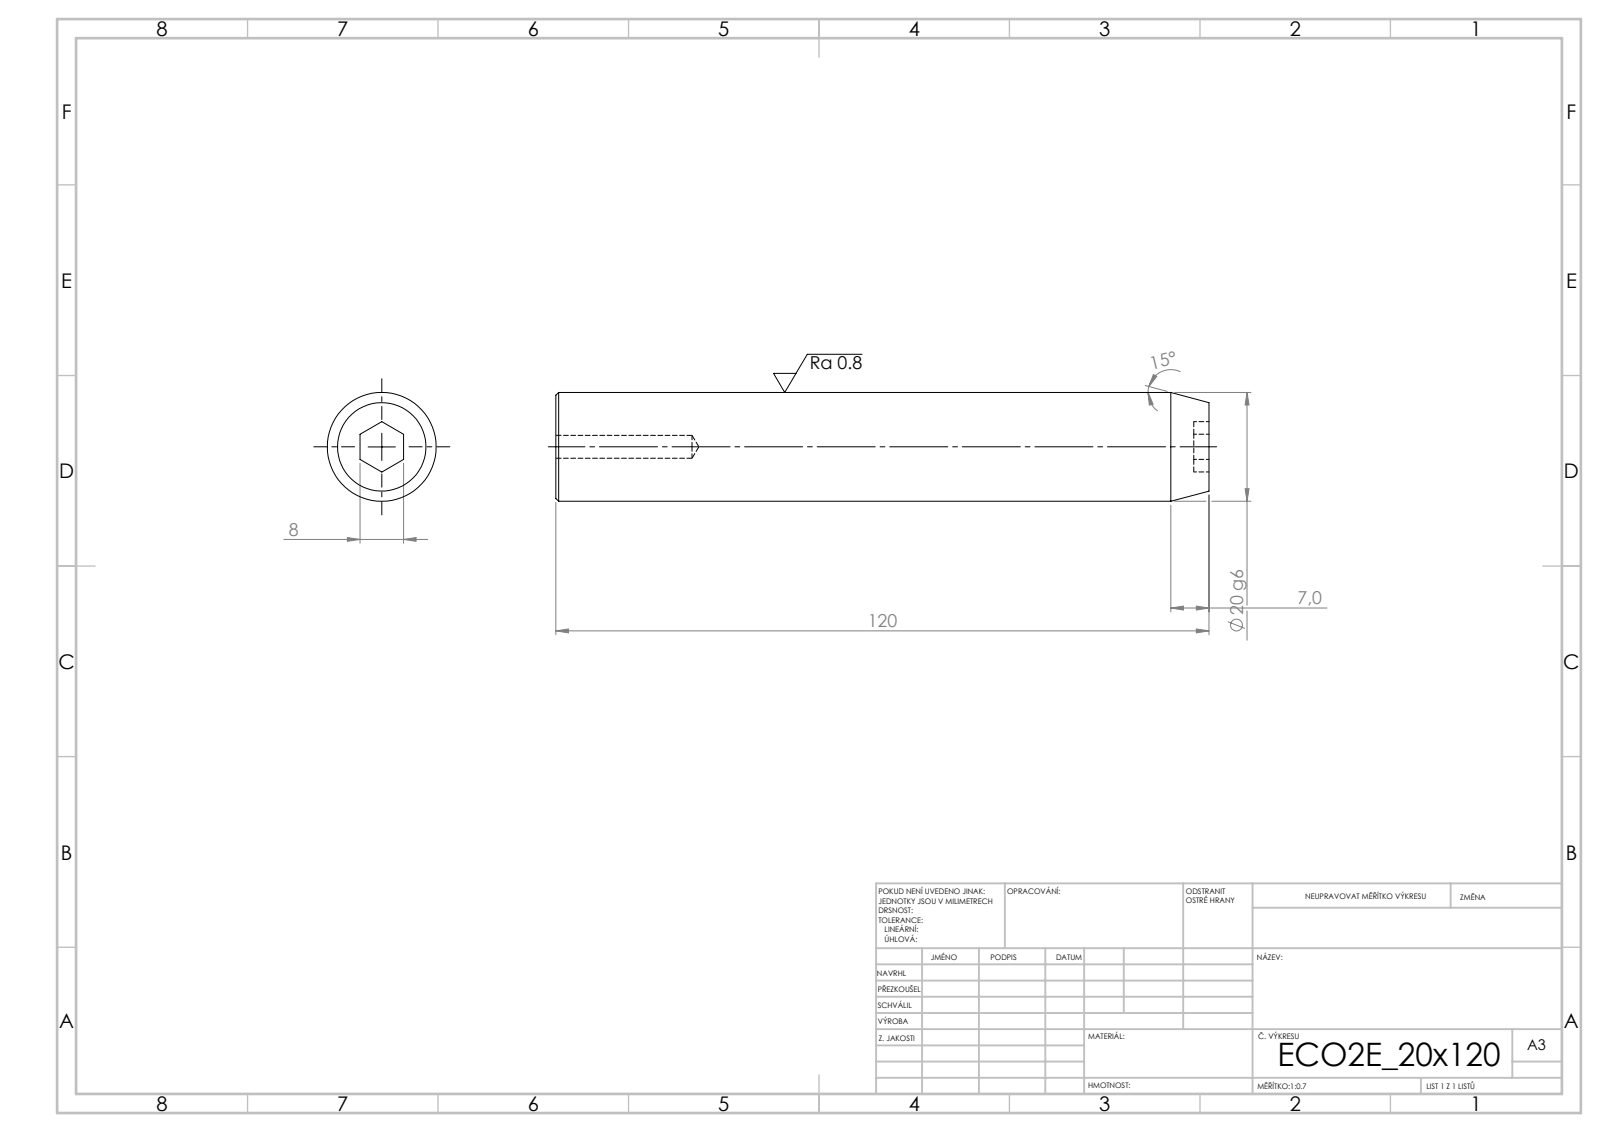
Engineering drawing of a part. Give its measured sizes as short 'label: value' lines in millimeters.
written by: SolidWorks 2019 (CONFIG_CONTROL_DESIGN)
unit: mm
bodies: 1 solid, 19 faces (9 planar, 4 cylindrical, 6 other)
size: 120 × 20 × 20
volume: 36 797 mm³; area: 8 425 mm²
holes: 1× ⌀4.2
bosses: 1× ⌀20
face distances: 120, 2.8, 117.2, 8
